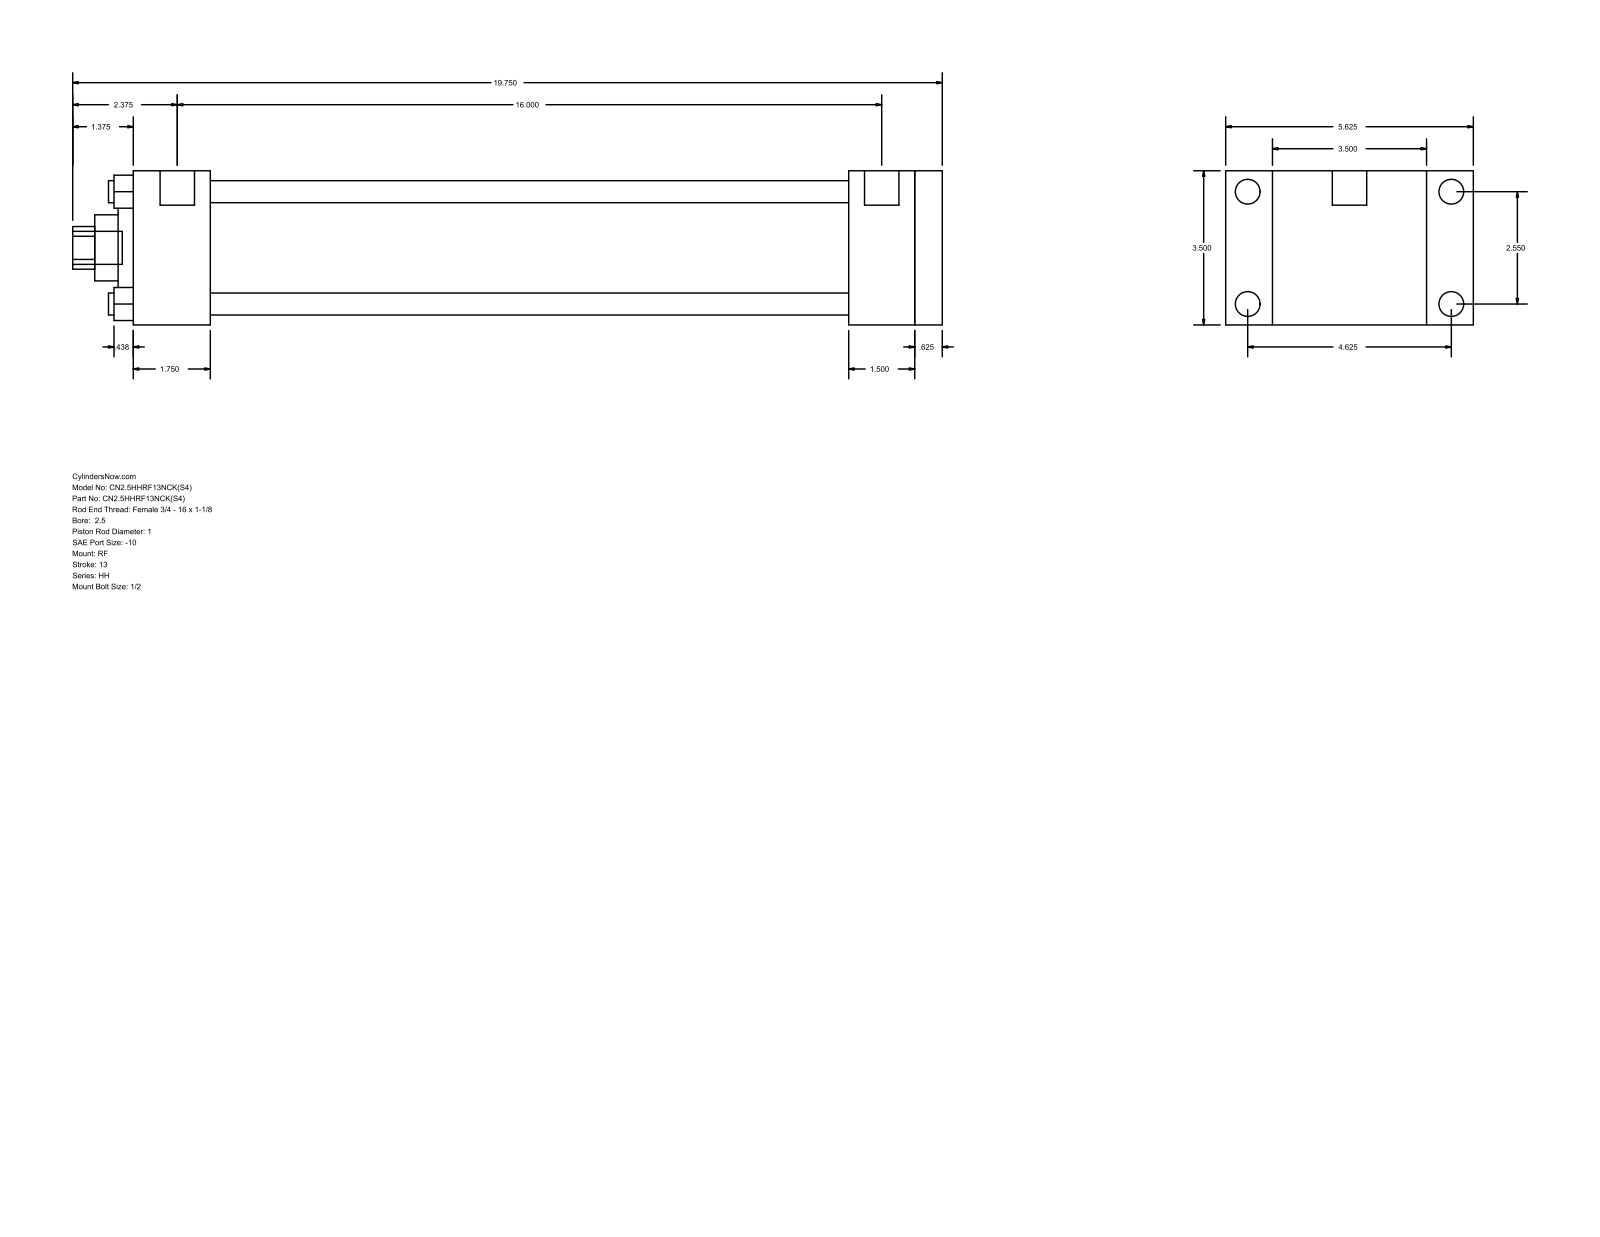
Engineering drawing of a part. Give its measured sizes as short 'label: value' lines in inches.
name: HH_RF__0250_1
written by: GSSL Pune (CONFIG_CONTROL_DESIGN)
unit: in
bodies: 0 solids, 94 faces (65 planar, 29 cylindrical, 0 other)
size: 19.75 × 5.625 × 3.5
holes: 4× ⌀0.5, 1× ⌀1, 1× ⌀1.5, 1× ⌀2.375, 1× ⌀2.875
bosses: 4× ⌀0.563, 4× ⌀0.219, 2× ⌀0.781, 1× ⌀0.75
rounds: 1× R0.484
face distances: 3.5, 0.625, 17.75, 18.375, 1.75, 16, 16.625, 16.25, 14.5, 1.5
hole spacings: 1.803, 2.55, 3.606
